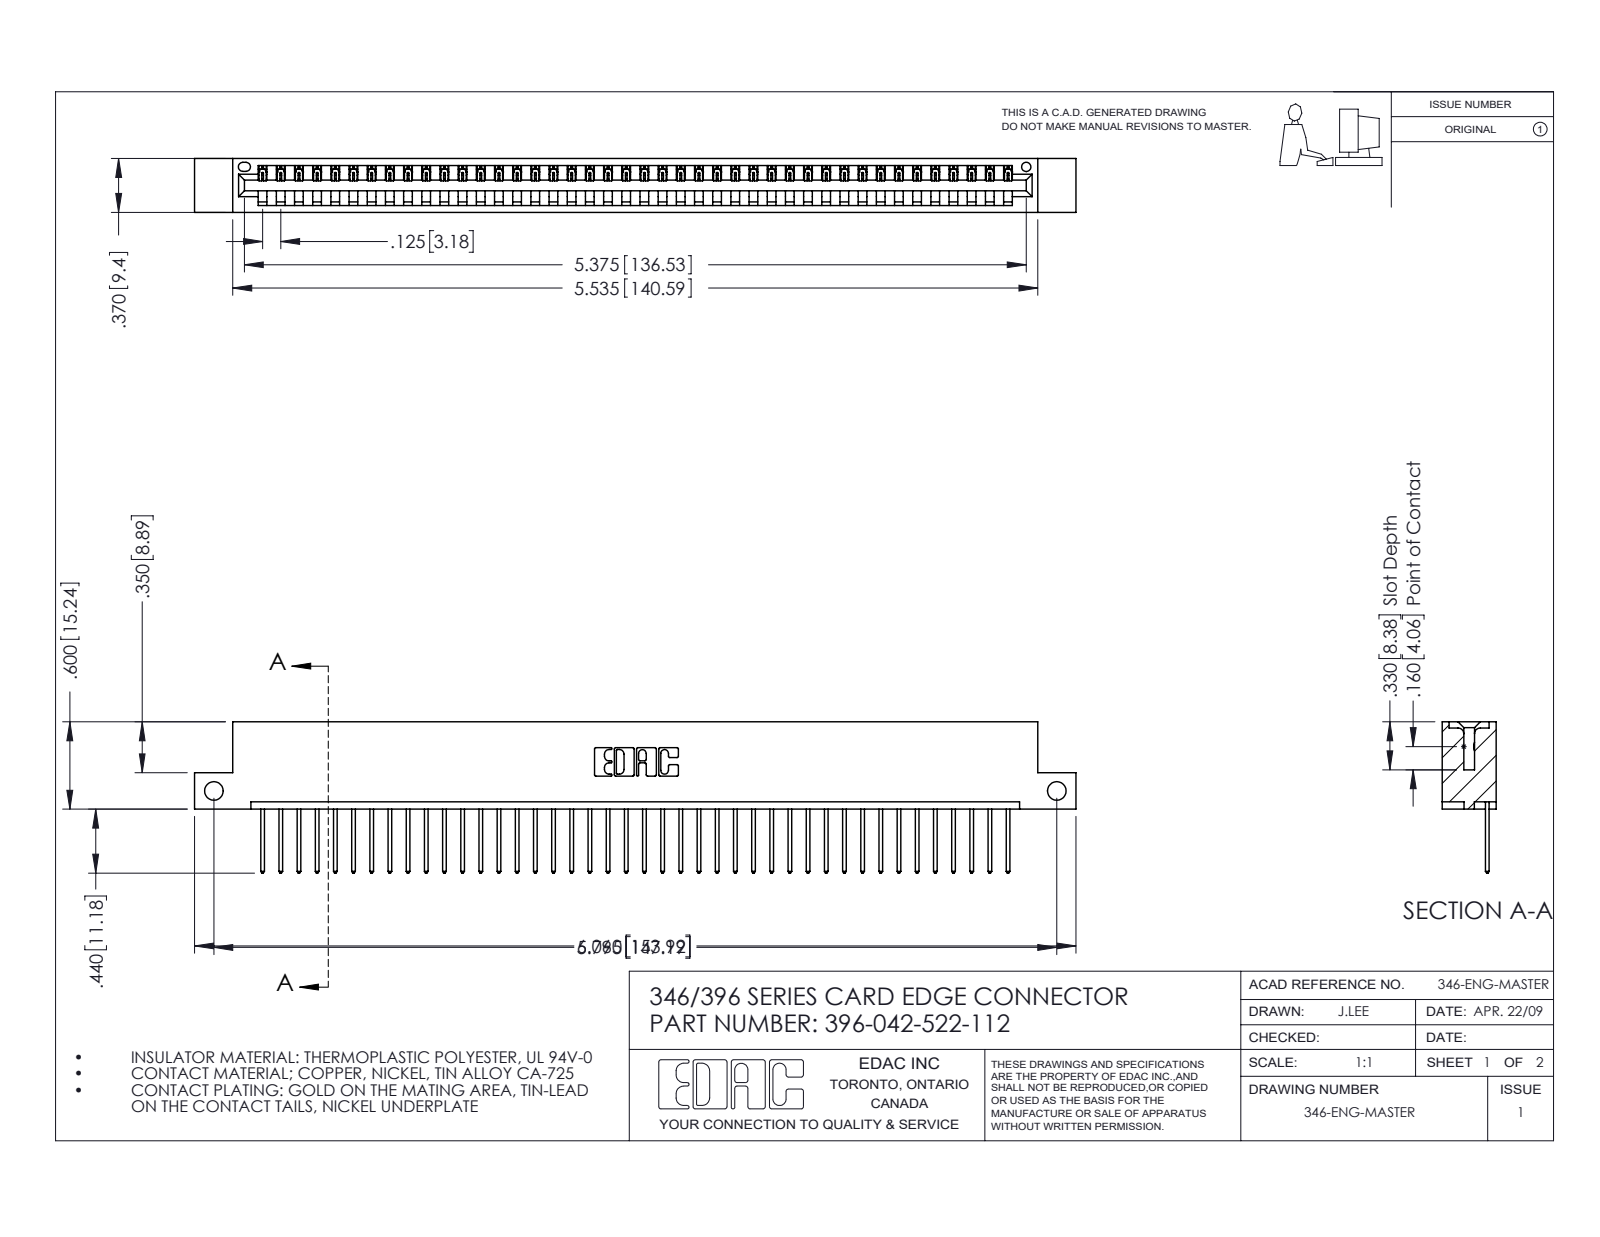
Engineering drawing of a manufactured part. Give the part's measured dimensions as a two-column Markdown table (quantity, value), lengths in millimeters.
| quantity | value |
| --- | --- |
| part name | 345-292-001_345-293-122; 396-042-522-112; 346 Part_Flush Mounting Lugs - Side Mount |
| STEP written by | SolidWorks 2016 (CONFIG_CONTROL_DESIGN) |
| units | millimeters |
| bodies | 43 solids, 2558 faces (1756 planar, 802 cylindrical, 0 other) |
| overall size | 153.9 × 26.4 × 9.4 |
| volume | 14 700 mm³ |
| surface area | 18 320 mm² |
| round holes (diameter × count) | 3.3 × 2, 1.6 × 1 |
| partial cylindrical surfaces (radius × count) | 0.2 × 84, 0.3 × 84, 0.3 × 22, 0.2 × 6, 0.8 × 6, 0.7 × 3, 0.8 × 2, 1 × 2 |
| main face-to-face distances | 1.2, 8.2, 9.4, 6.4, 1.8, 7.6, 0.6, 3.8, 5.6, 2.5 |
| hole center spacings | 147.2 |
